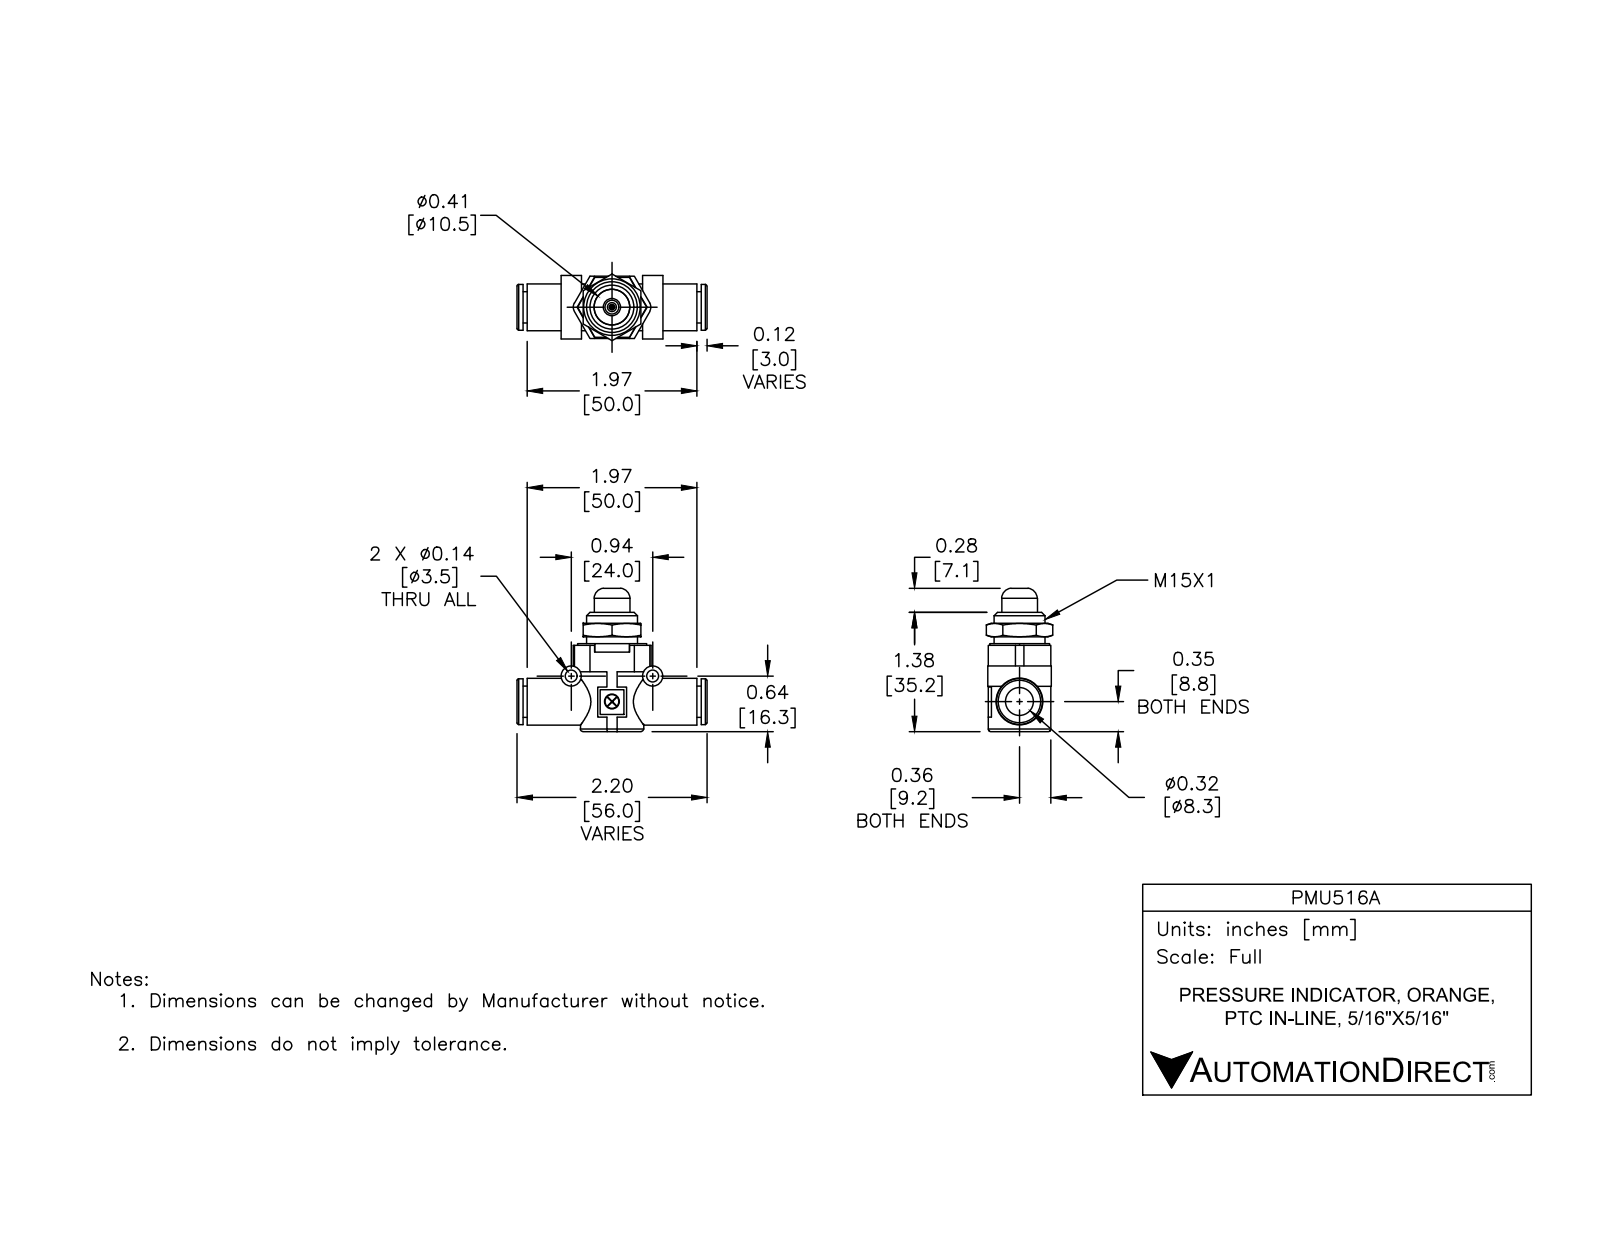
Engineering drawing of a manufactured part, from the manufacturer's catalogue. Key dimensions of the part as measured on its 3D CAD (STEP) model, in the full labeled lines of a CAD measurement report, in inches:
Part name (STEP PRODUCT): PMU516A
STEP written by: SolidWorks 2015 (CONFIG_CONTROL_DESIGN)
Units: inches
Bodies: 7 solids, 175 faces (82 planar, 59 cylindrical, 34 other)
Overall size (bounding box): 2.205 × 1.663 × 0.773
Volume: 0.811 in³ · Surface area: 15.72 in²
Round holes (diameter × count): ⌀0.138 ×2, ⌀0.028 ×1, ⌀0.106 ×1, ⌀0.157 ×1, ⌀0.161 ×1, ⌀0.325 ×1, ⌀0.368 ×1, ⌀0.37 ×1, ⌀0.413 ×1
Round bosses / shafts (diameter × count): ⌀0.236 ×2, ⌀0.734 ×1, ⌀0.591 ×1, ⌀0.543 ×1, ⌀0.531 ×1, ⌀0.413 ×1, ⌀0.364 ×1, ⌀0.173 ×1
Partial cylindrical surfaces — rounded edges, fillets, slot ends (radius × count): R0.03 ×2, R0.098 ×2
Main face-to-face distances: 0.335, 0.921, 0.069, 1.256, 1.098, 0.177, 0.157, 0.049, 0.079, 2.018
Hole centre spacings: 0.557, 0.945
